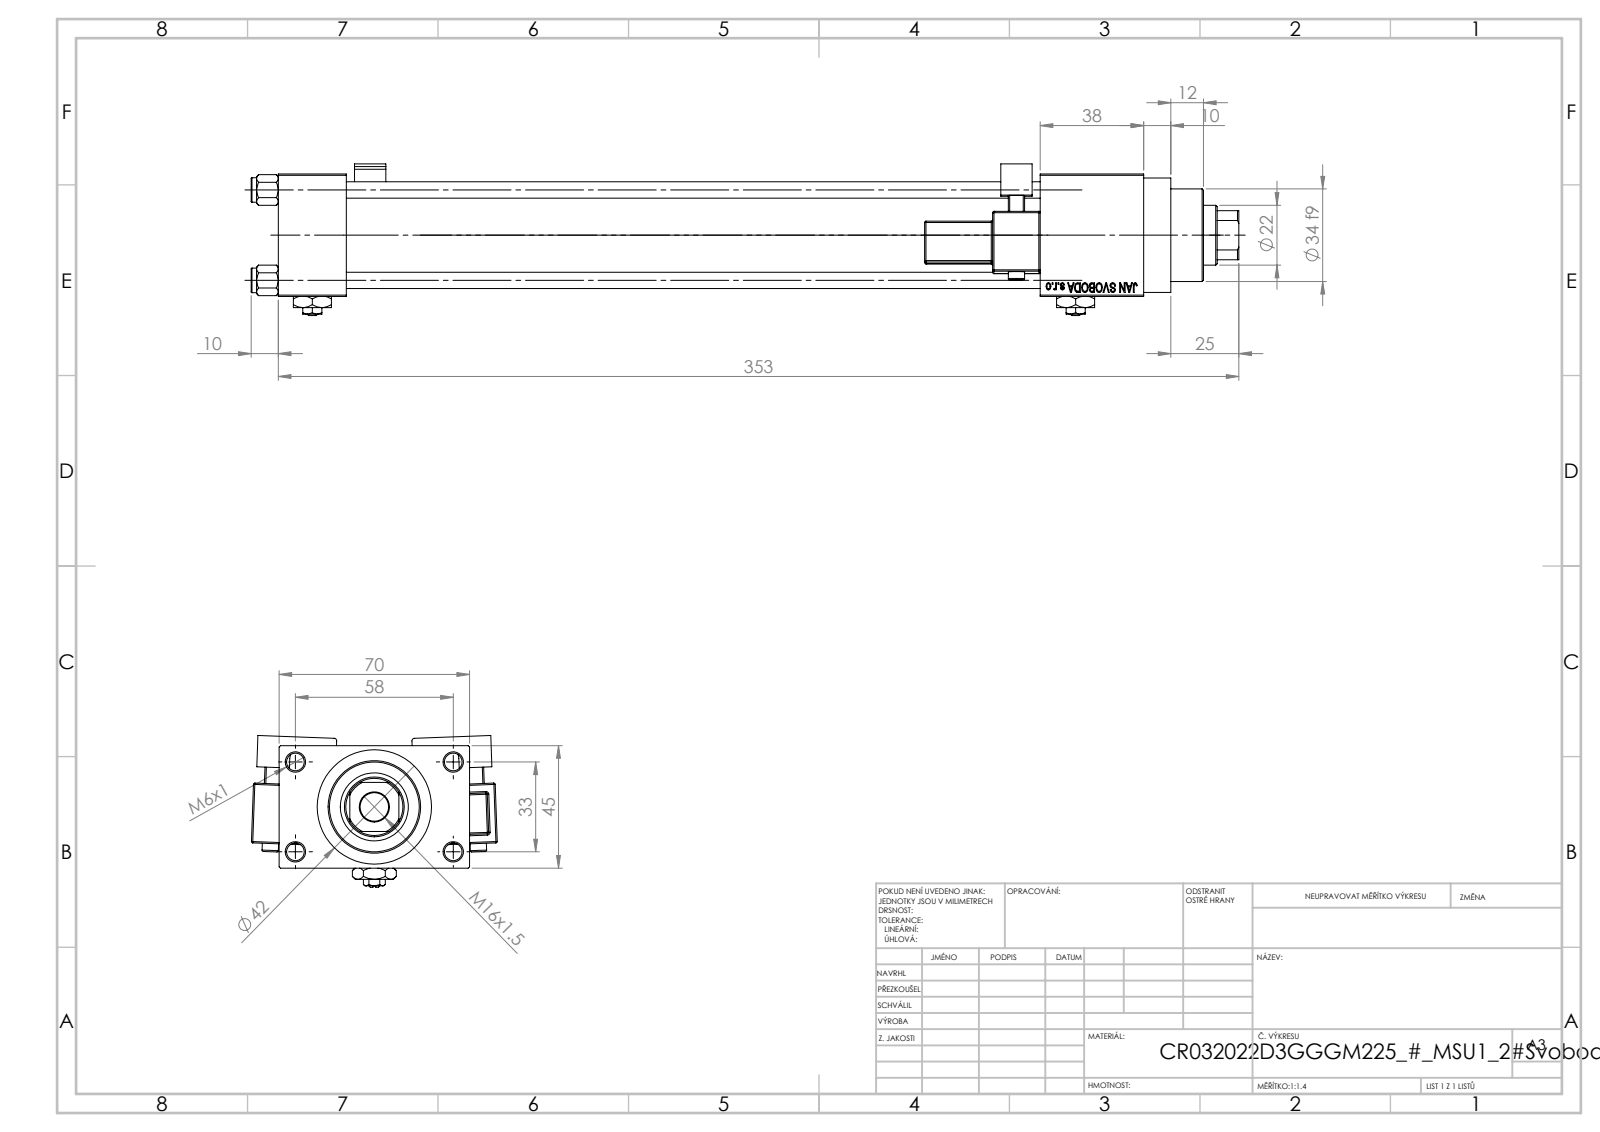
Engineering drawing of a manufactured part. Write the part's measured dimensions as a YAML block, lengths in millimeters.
part_name: "NUT_M5_D; V215CR_MSU; V215CR_D_TYCINKA; Zatka_pro_OIL_PORT (+3 more)"
step_written_by: "SolidWorks 2019 (CONFIG_CONTROL_DESIGN)"
units: millimeters
bodies: {solids: 15, faces: 1360, planar: 604, cylindrical: 160, other: 596}
overall_size: [363, 90.31, 55.72]
volume: 452760
surface_area: 167907
round_holes:
  - {diameter: 6, count: 4}
  - {diameter: 6.5, count: 4}
  - {diameter: 7, count: 2}
  - {diameter: 13.16, count: 2}
  - {diameter: 20, count: 2}
  - {diameter: 10.5, count: 1}
  - {diameter: 22, count: 1}
  - {diameter: 24, count: 1}
  - {diameter: 25, count: 1}
  - {diameter: 32, count: 1}
  - {diameter: 33, count: 1}
round_bosses_or_shafts:
  - {diameter: 9, count: 4}
  - {diameter: 6, count: 2}
  - {diameter: 42, count: 1}
  - {diameter: 38, count: 1}
  - {diameter: 34, count: 1}
partial_cylinders:
  - {radius: 0.5, count: 48}
  - {radius: 1, count: 2}
  - {radius: 2.5, count: 2}
  - {radius: 4, count: 2}
  - {radius: 10.5, count: 1}
face_to_face_distances: [45, 25, 12.5, 255, 3, 57.5, 280, 38, 293, 70]
hole_center_spacings: [12.4, 23.48, 33.2, 33.37, 35.35, 45.6, 56.35, 33]
